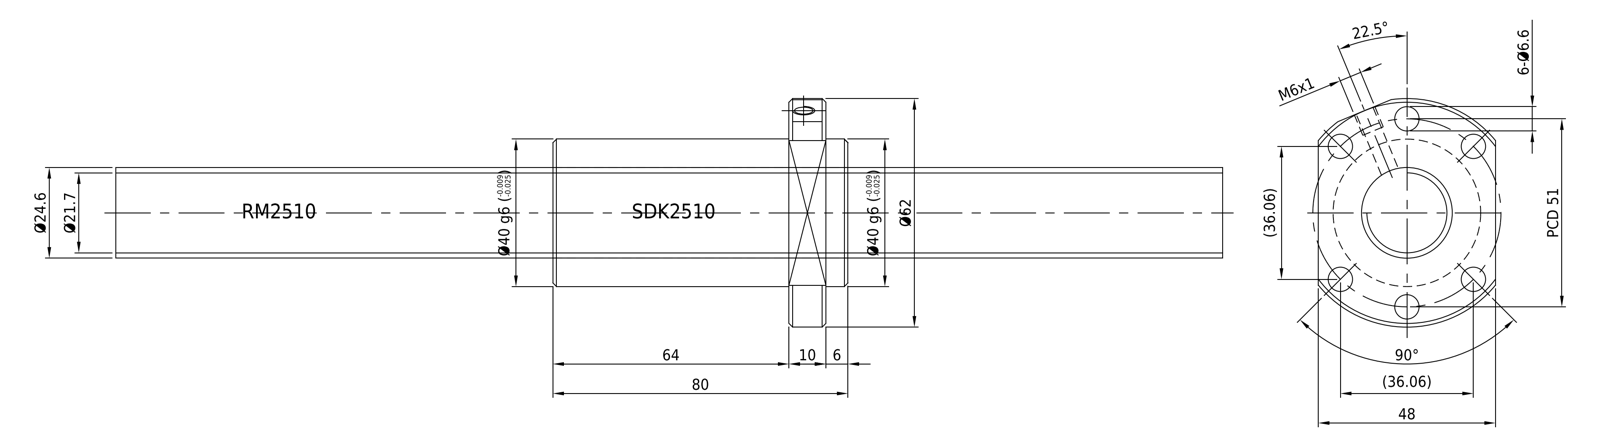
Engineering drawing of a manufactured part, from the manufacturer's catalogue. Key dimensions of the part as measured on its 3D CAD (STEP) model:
Part name (STEP PRODUCT): RM2510; SDK2510
STEP written by: SolidWorks 2013 (CONFIG_CONTROL_DESIGN)
Units: millimetres
Bodies: 2 solids, 48 faces (9 planar, 27 cylindrical, 12 other)
Overall size (bounding box): 300 × 62 × 48
Volume: 215 014 mm³ · Surface area: 46 178 mm²
Round holes (diameter × count): ⌀6.6 ×6, ⌀4.44 ×1, ⌀5 ×1, ⌀25 ×1
Round bosses / shafts (diameter × count): ⌀40 ×1, ⌀24.6 ×1
Partial cylindrical surfaces — rounded edges, fillets, slot ends (radius × count): R31 ×1
Main face-to-face distances: 10, 110, 190, 74, 64, 6, 16, 80, 116, 126
Hole centre spacings: 25.5, 19.52, 36.06, 47.12, 51
